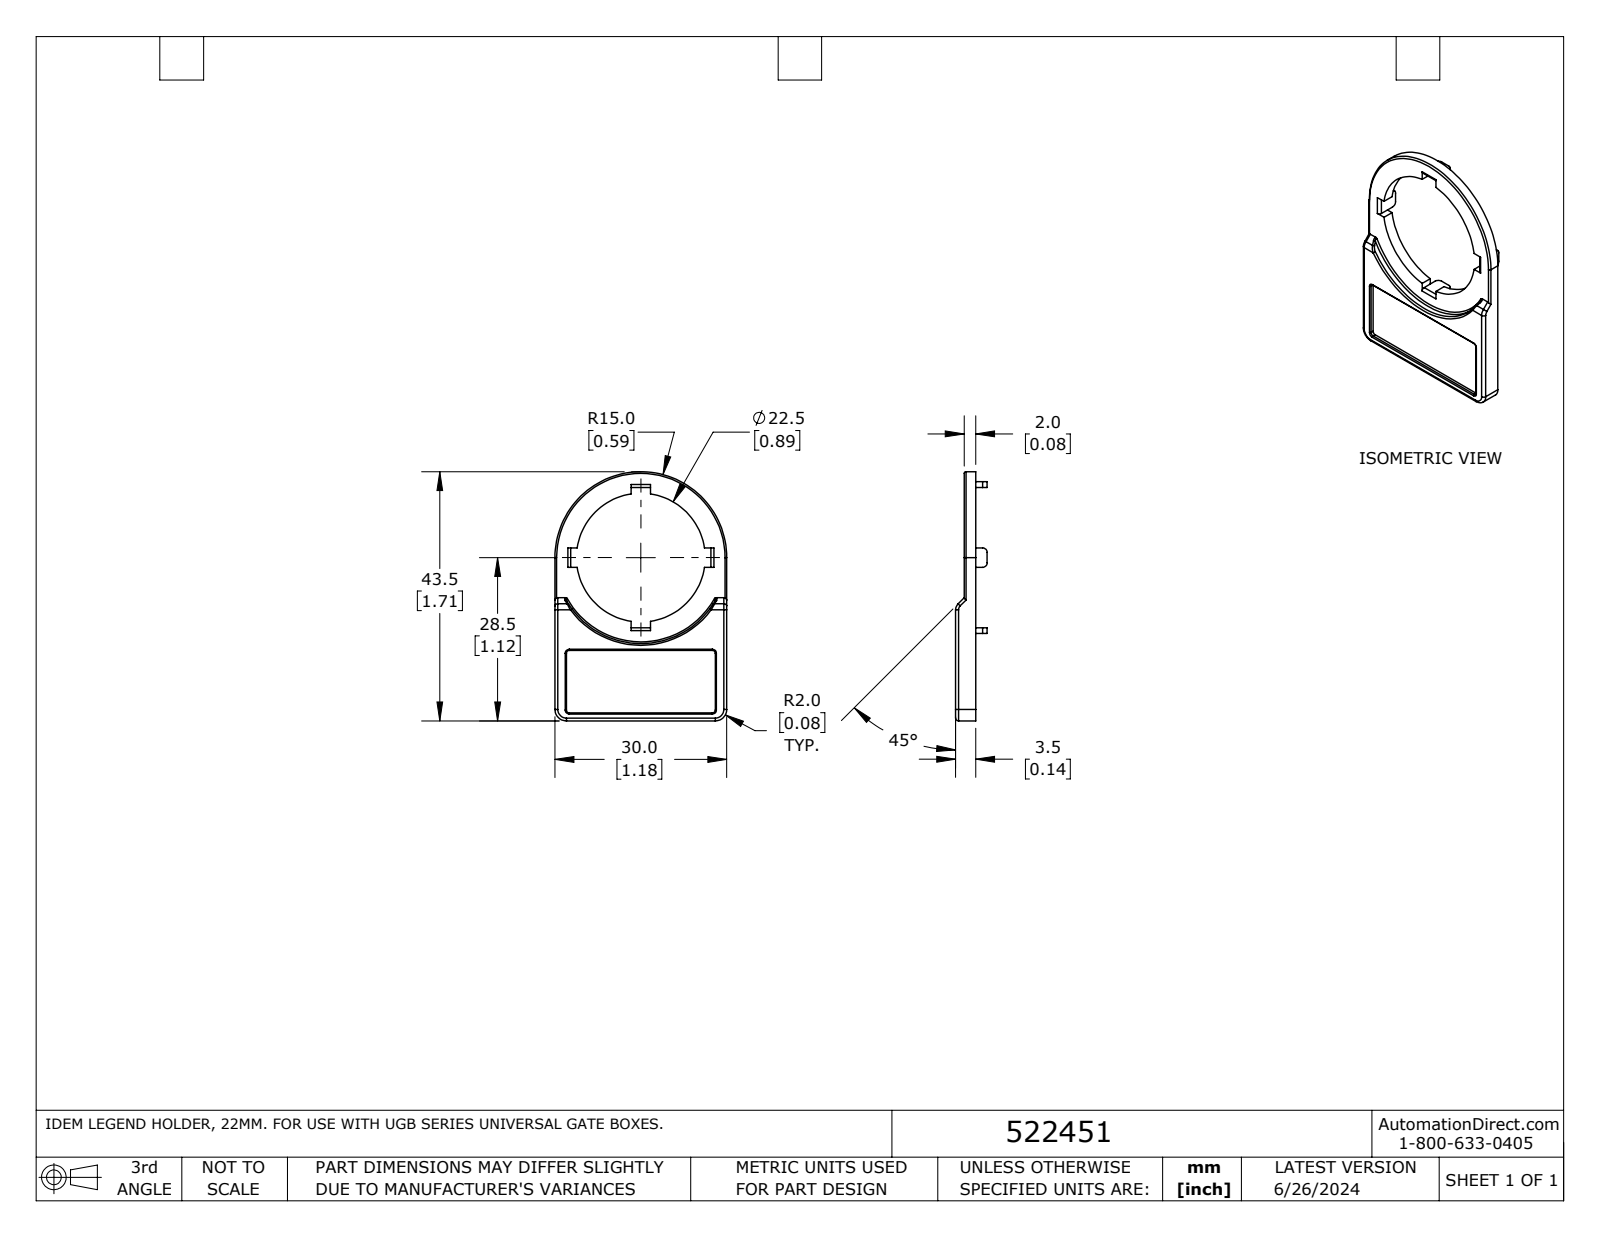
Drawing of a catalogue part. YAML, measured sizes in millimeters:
part_name: "522451 Legend Holder for use with 22mm Devices"
step_written_by: "SolidWorks 2024 (CONFIG_CONTROL_DESIGN)"
units: millimeters
bodies: {solids: 1, faces: 261, planar: 85, cylindrical: 115, other: 61}
overall_size: [43.5, 30, 5.5]
volume: 1683
surface_area: 2571
round_holes:
  - {diameter: 22.5, count: 1}
  - {diameter: 30, count: 1}
partial_cylinders:
  - {radius: 0.3, count: 34}
  - {radius: 0.2, count: 21}
  - {radius: 0.5, count: 15}
  - {radius: 0.8, count: 4}
  - {radius: 0.6, count: 2}
  - {radius: 2, count: 2}
  - {radius: 1.5, count: 1}
  - {radius: 16.4, count: 1}
face_to_face_distances: [0.8, 2, 2.8, 1.6, 0.4, 1.2, 3.5, 1.9, 1.5, 0.7]
